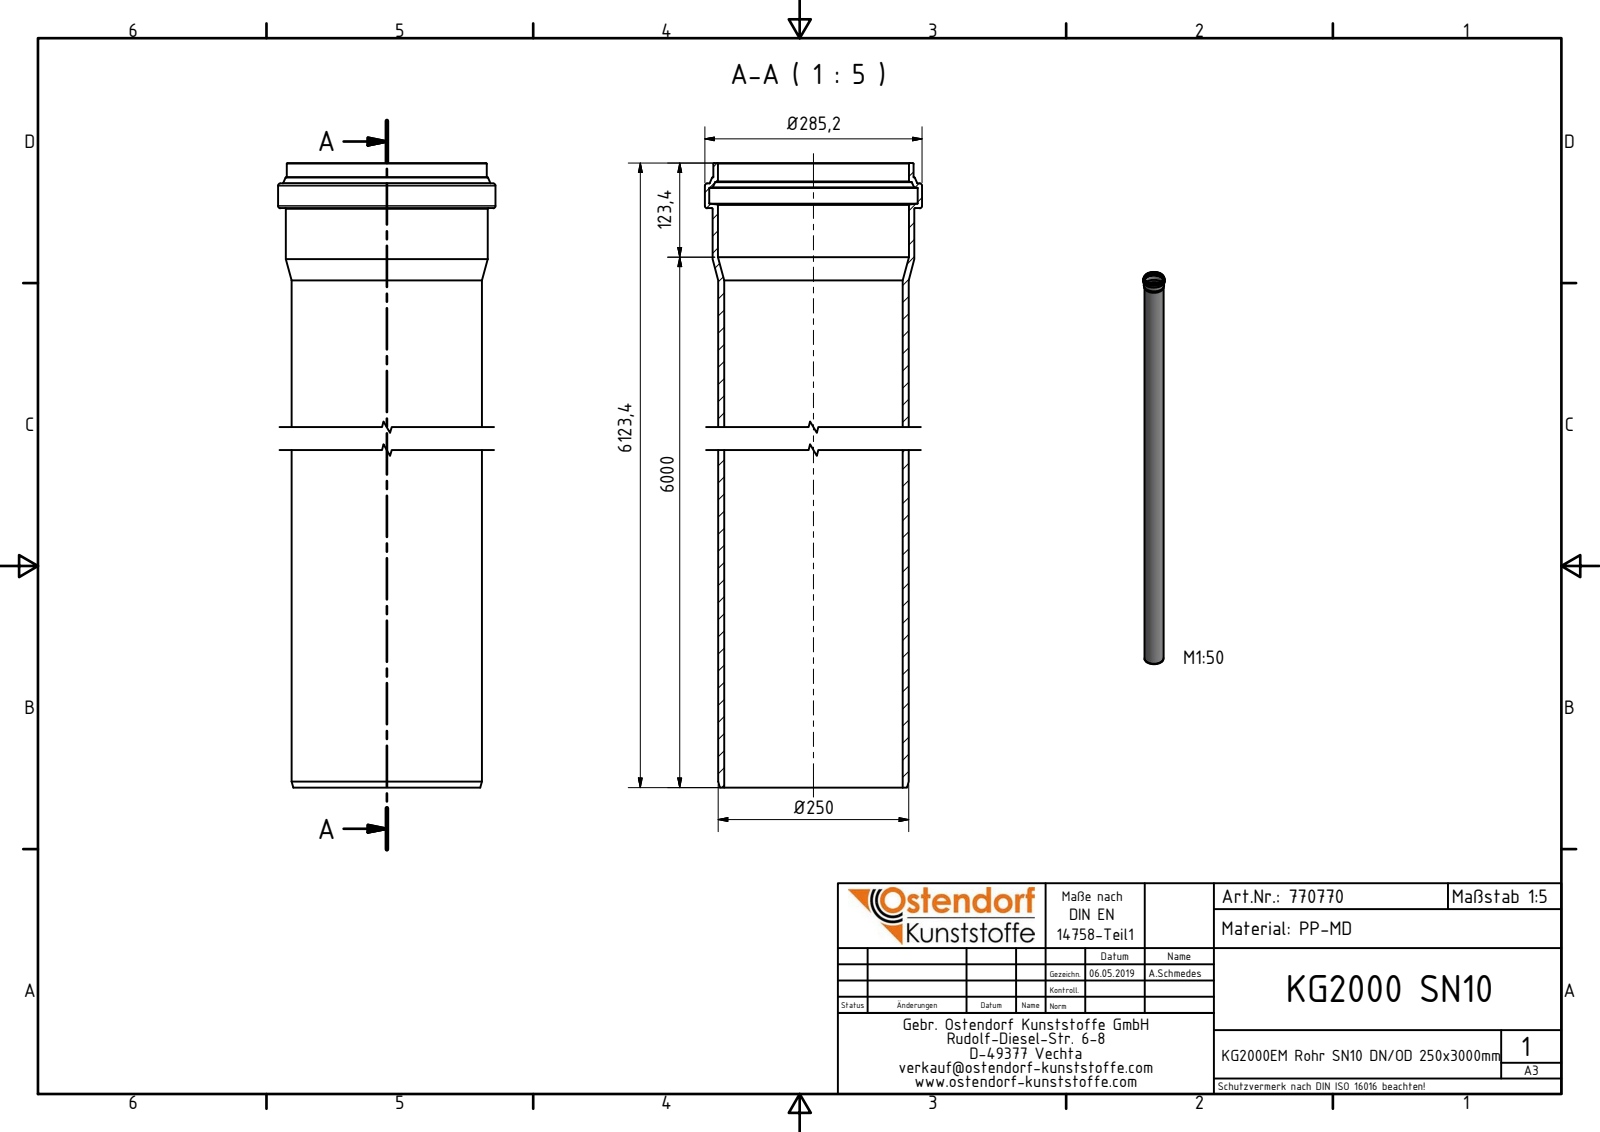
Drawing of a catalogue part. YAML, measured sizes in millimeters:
part_name: "770790 KG2000EM Rohr SN10 DN-OD250x6000"
step_written_by: "Autodesk Inventor 2016 (AUTOMOTIVE_DESIGN)"
units: millimeters
bodies: {solids: 1, faces: 35, planar: 5, cylindrical: 8, other: 22}
overall_size: [6123.4, 285.2, 285.2]
volume: 35910000
surface_area: 9377000
round_holes:
  - {diameter: 234.6, count: 1}
  - {diameter: 251, count: 1}
  - {diameter: 273.6, count: 1}
round_bosses_or_shafts:
  - {diameter: 285.2, count: 1}
  - {diameter: 265, count: 1}
  - {diameter: 262.6, count: 1}
  - {diameter: 250, count: 1}
face_to_face_distances: [6064.2, 6123.4, 59.2, 6096.7, 32.5, 26.7, 6104.53, 40.33, 7.83, 18.87]
